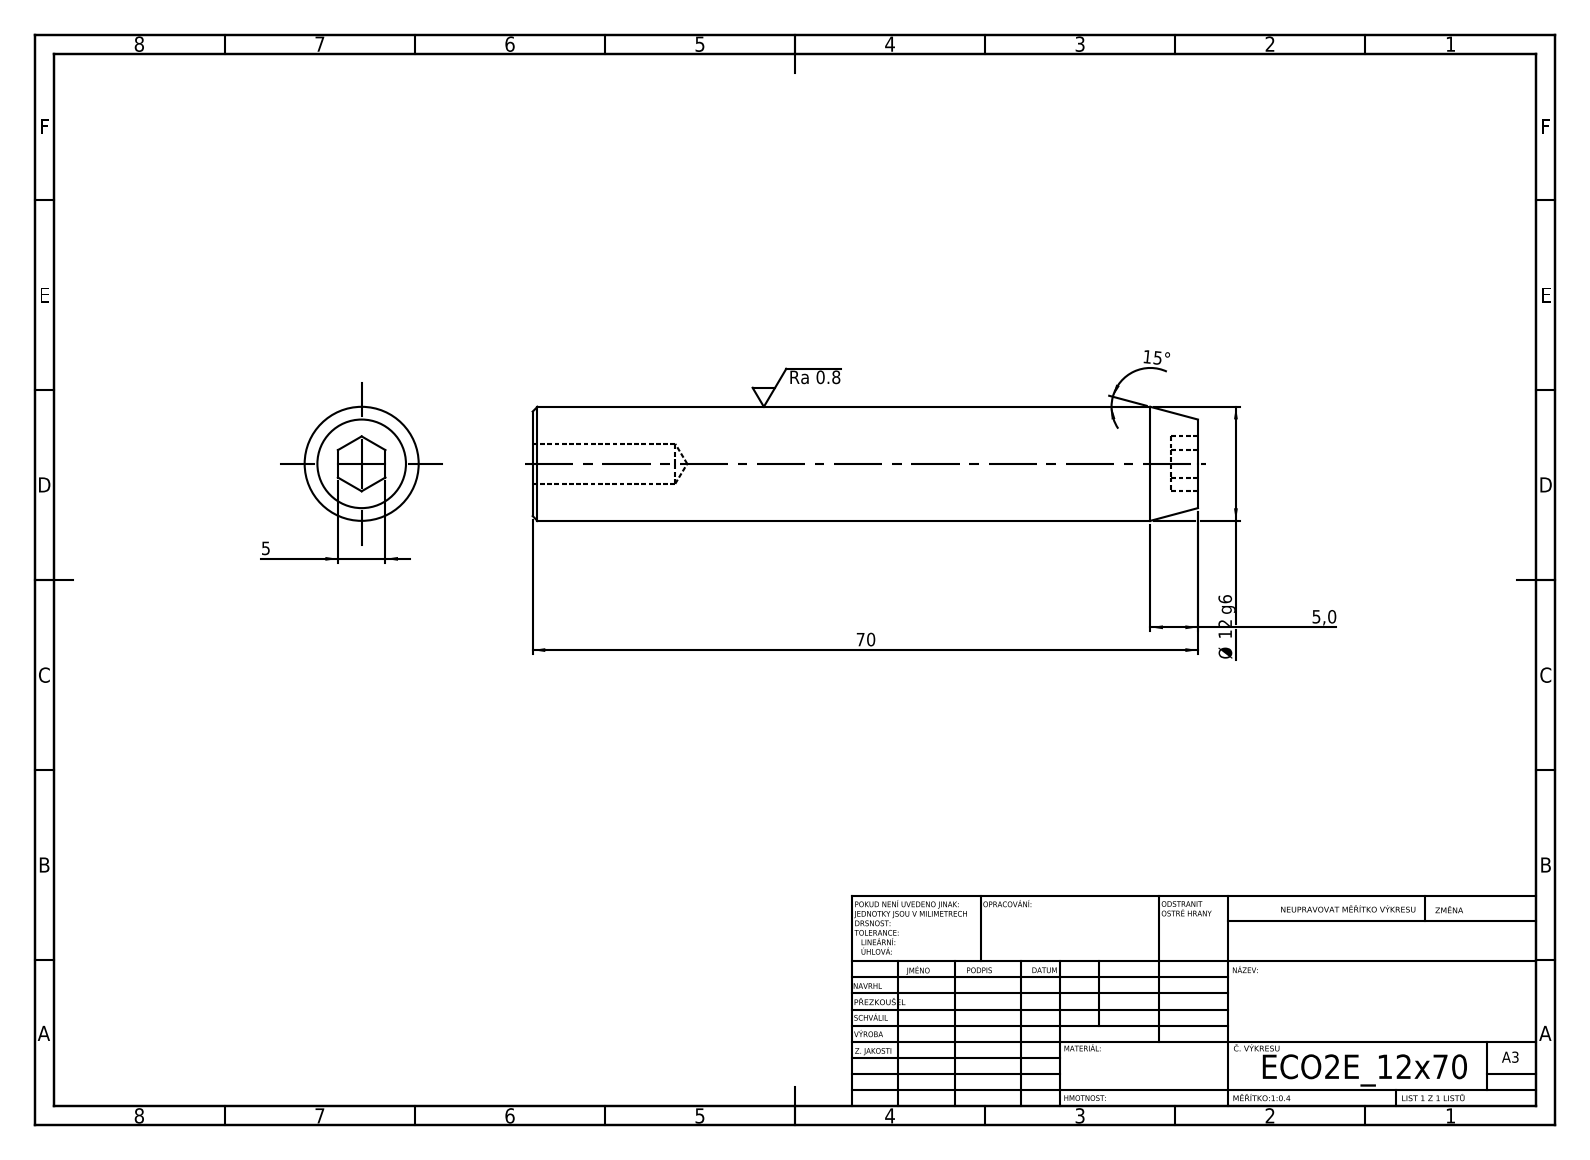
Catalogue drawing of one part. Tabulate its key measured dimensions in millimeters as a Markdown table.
| quantity | value |
| --- | --- |
| STEP written by | SolidWorks 2019 (CONFIG_CONTROL_DESIGN) |
| units | millimeters |
| bodies | 1 solid, 19 faces (9 planar, 4 cylindrical, 6 other) |
| overall size | 70 × 12 × 12 |
| volume | 7 521 mm³ |
| surface area | 3 042 mm² |
| round holes (diameter × count) | 4.2 × 1 |
| round bosses / shafts (diameter × count) | 12 × 1 |
| main face-to-face distances | 70, 5, 2.8, 67.2 |
